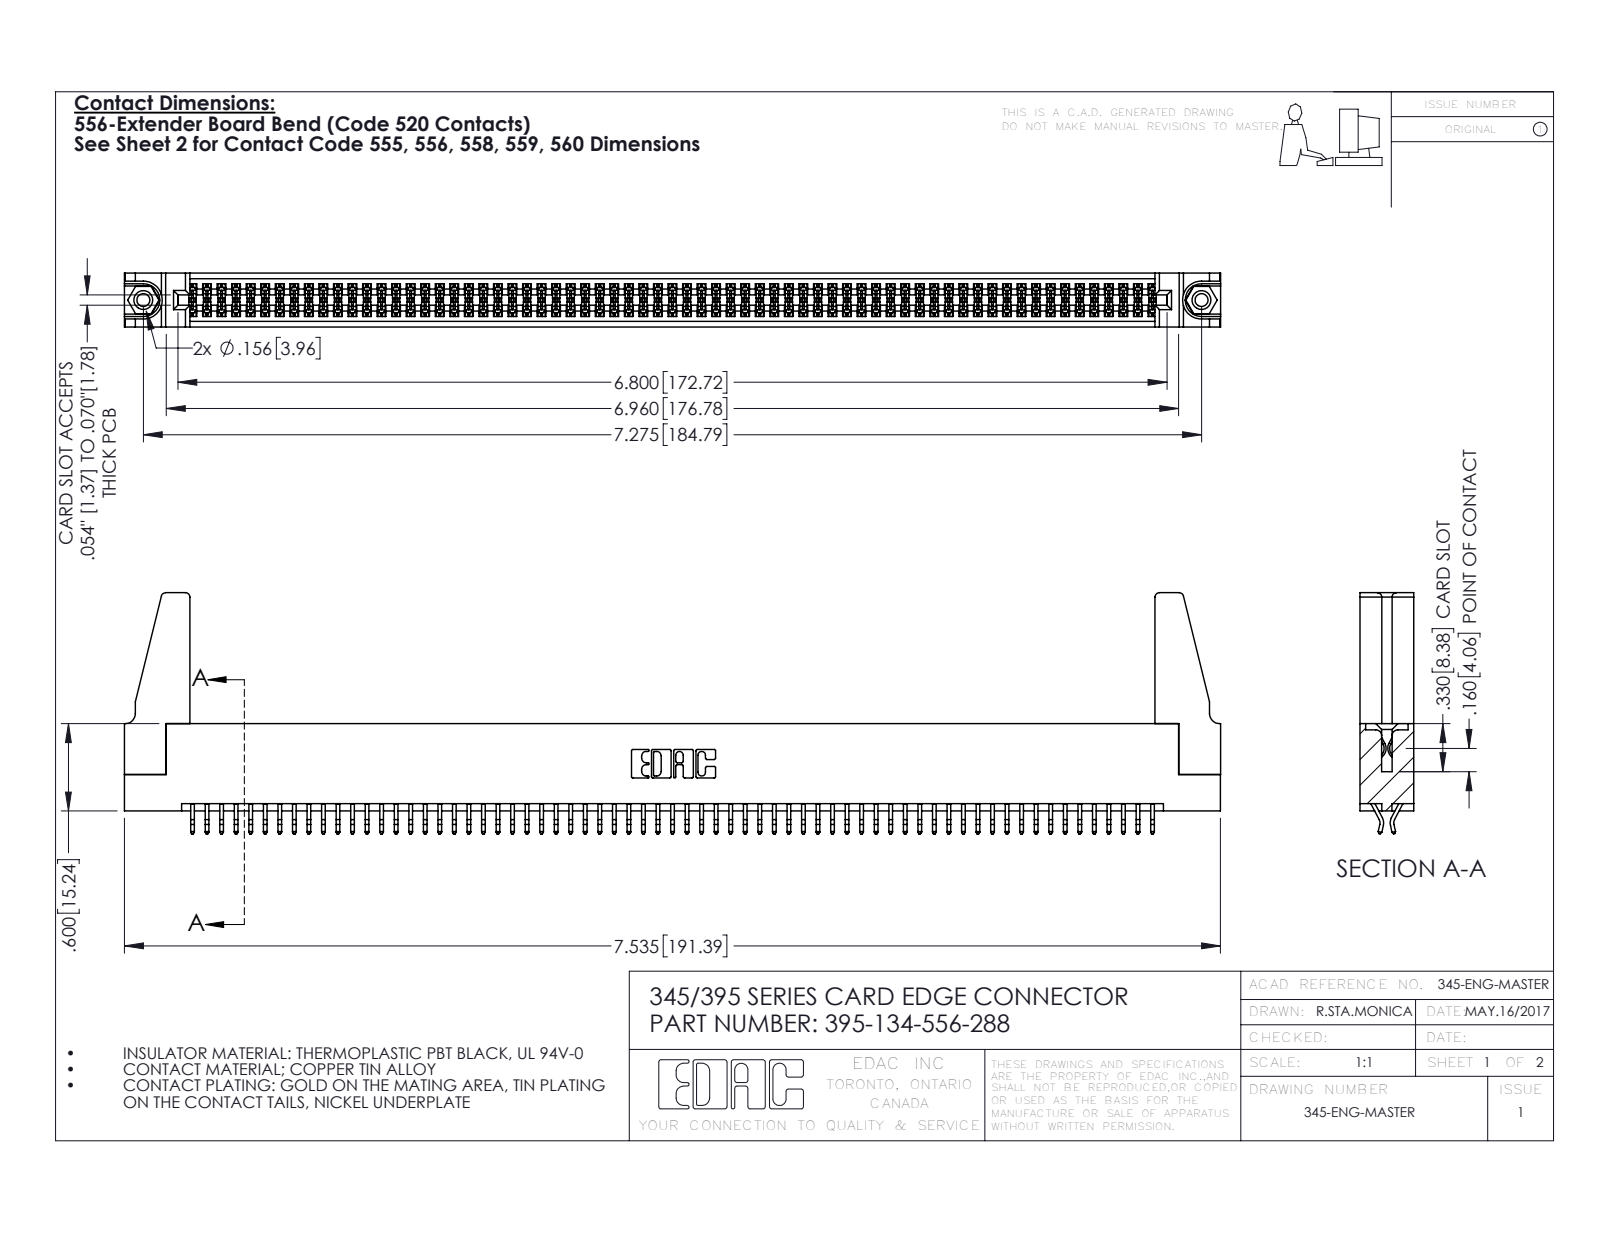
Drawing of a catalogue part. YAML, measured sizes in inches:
part_name: "345-220-078_345-220-088; 395-134-556-288; 345-292-001_556 Tail; 345-250-001_345-250-001-102 (+1 more)"
step_written_by: "SolidWorks 2016 (CONFIG_CONTROL_DESIGN)"
units: inches
bodies: {solids: 139, faces: 7754, planar: 5110, cylindrical: 2628, other: 16}
overall_size: [7.536, 1.657, 0.37]
volume: 1.347
surface_area: 48.53
round_holes:
  - {diameter: 0.089, count: 2}
  - {diameter: 0.125, count: 2}
  - {diameter: 0.156, count: 2}
  - {diameter: 0.064, count: 1}
round_bosses_or_shafts:
  - {diameter: 0.155, count: 2}
partial_cylinders:
  - {radius: 0.006, count: 201}
  - {radius: 0.01, count: 22}
  - {radius: 0.03, count: 8}
  - {radius: 0.007, count: 6}
  - {radius: 0.031, count: 6}
  - {radius: 0.026, count: 3}
  - {radius: 0.01, count: 2}
  - {radius: 0.014, count: 2}
face_to_face_distances: [0.072, 0.298, 0.37, 0.2, 0.025, 0.098, 0.272, 0.225, 0.175, 0.149]
hole_center_spacings: [0.27, 7.039, 7.275]
